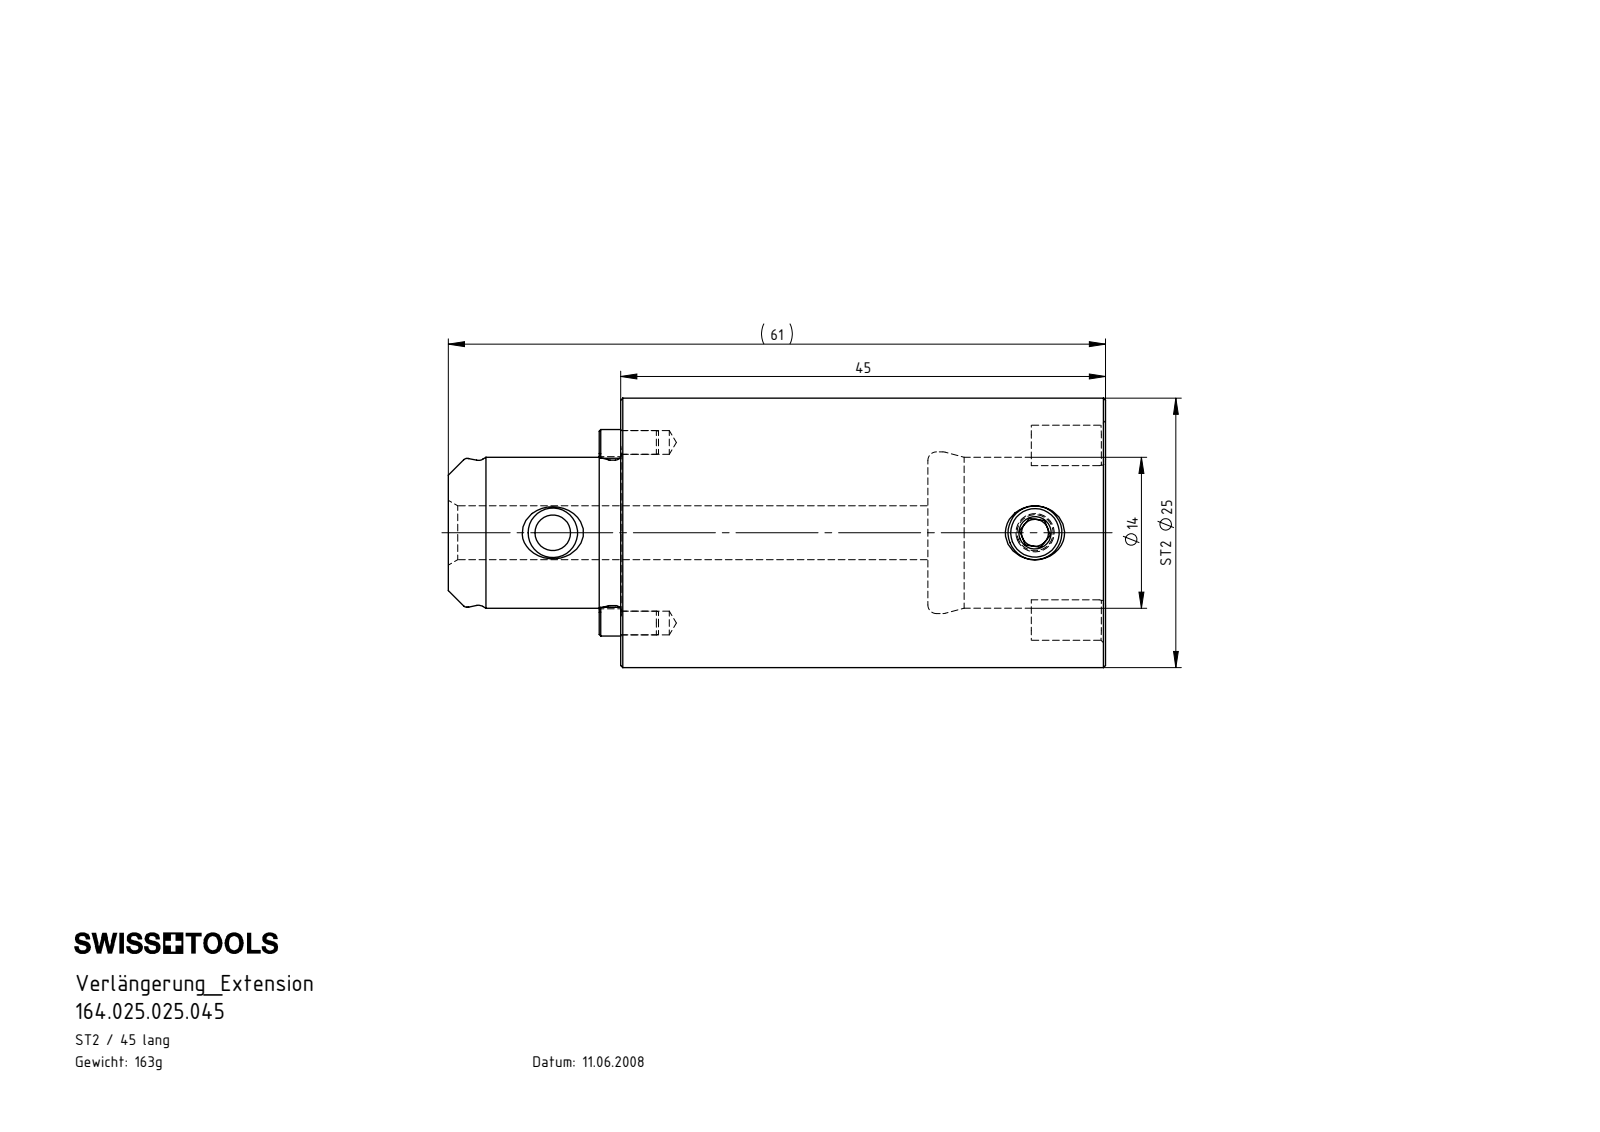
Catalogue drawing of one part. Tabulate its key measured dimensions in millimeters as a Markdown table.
| quantity | value |
| --- | --- |
| part name | ST2-ER2.001.006_A; ST2-ER1.001.006_A; ST2-ST2.K01.045; ST2-ST2.K01.045_A |
| STEP written by | SolidWorks 2015 (CONFIG_CONTROL_DESIGN) |
| units | millimeters |
| bodies | 4 solids, 146 faces (26 planar, 43 cylindrical, 77 other) |
| overall size | 61 × 25 × 25 |
| volume | 20 799 mm³ |
| surface area | 6 988 mm² |
| round holes (diameter × count) | 2.2 × 2, 3.3 × 1, 4.5 × 1, 5 × 1, 14 × 1, 15 × 1 |
| round bosses / shafts (diameter × count) | 25 × 1, 13.8 × 1, 13.5 × 1, 5 × 1, 2.2 × 1 |
| partial cylindrical surfaces (radius × count) | 0.5 × 4, 1.8 × 2, 1.98 × 2, 7.05 × 1 |
| main face-to-face distances | 45, 28.5, 16.5, 16, 44.5, 61, 11.78, 54.1, 38.1, 9.6 |
| hole center spacings | 8.38, 16.76, 44.75 |
